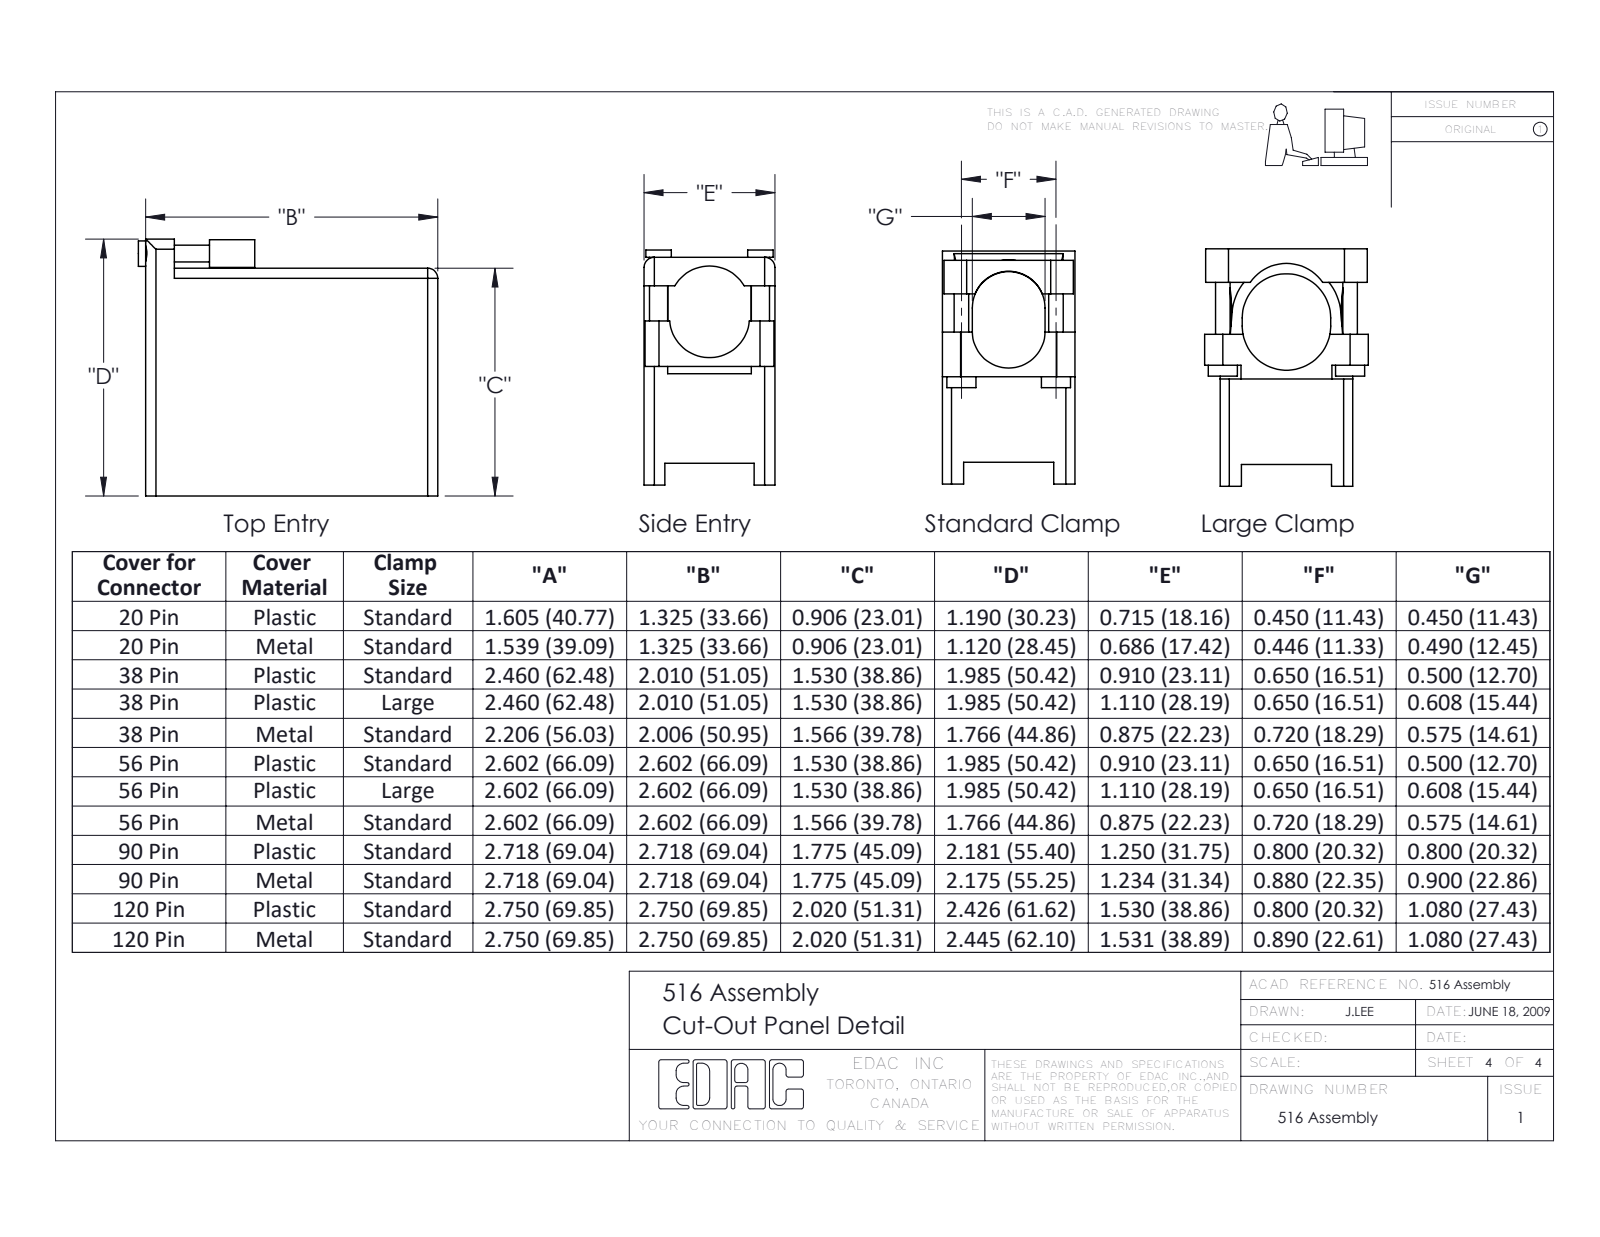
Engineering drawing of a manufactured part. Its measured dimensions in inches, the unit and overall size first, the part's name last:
Units: inches
Overall size (bounding box): 3.012 × 2.153 × 1.125
Round holes (diameter × count): ⌀0.13 ×57, ⌀0.05 ×16, ⌀0.187 ×4, ⌀0.122 ×2, ⌀0.125 ×2, ⌀0.125 ×2, ⌀0.133 ×2, ⌀0.101 ×1, ⌀0.163 ×1, ⌀0.208 ×1, ⌀0.265 ×1, ⌀0.265 ×1
Round bosses / shafts (diameter × count): ⌀0.2 ×2, ⌀0.1 ×2, ⌀0.203 ×1
Partial cylindrical surfaces — rounded edges, fillets, slot ends (radius × count): R0.022 ×140, R0.008 ×112, R0.016 ×112, R0.012 ×56, R0.007 ×28, R0.02 ×28, R0.08 ×28, R0.01 ×22
Main face-to-face distances: 0.05, 0.86, 0.15, 0.91, 0.81, 0.843, 0.017, 0.45, 0.225, 0.3
Hole centre spacings: 0.15, 0.26, 0.397, 0.3, 0.397, 0.26, 0.13, 0.52
Volume: 1.619 in³ · Surface area: 67.33 in²
Bodies: 59 solids, 5384 faces (3249 planar, 1776 cylindrical, 359 other)
Part name (STEP PRODUCT): 516-292-001_501 Contact; 516-230-001_Plastic - 056 Side Entry - Large Clamp; 516 Plug Insulator_056; 516-056-501-546 (+1 more)
STEP written by: SolidWorks 2020 (CONFIG_CONTROL_DESIGN)
